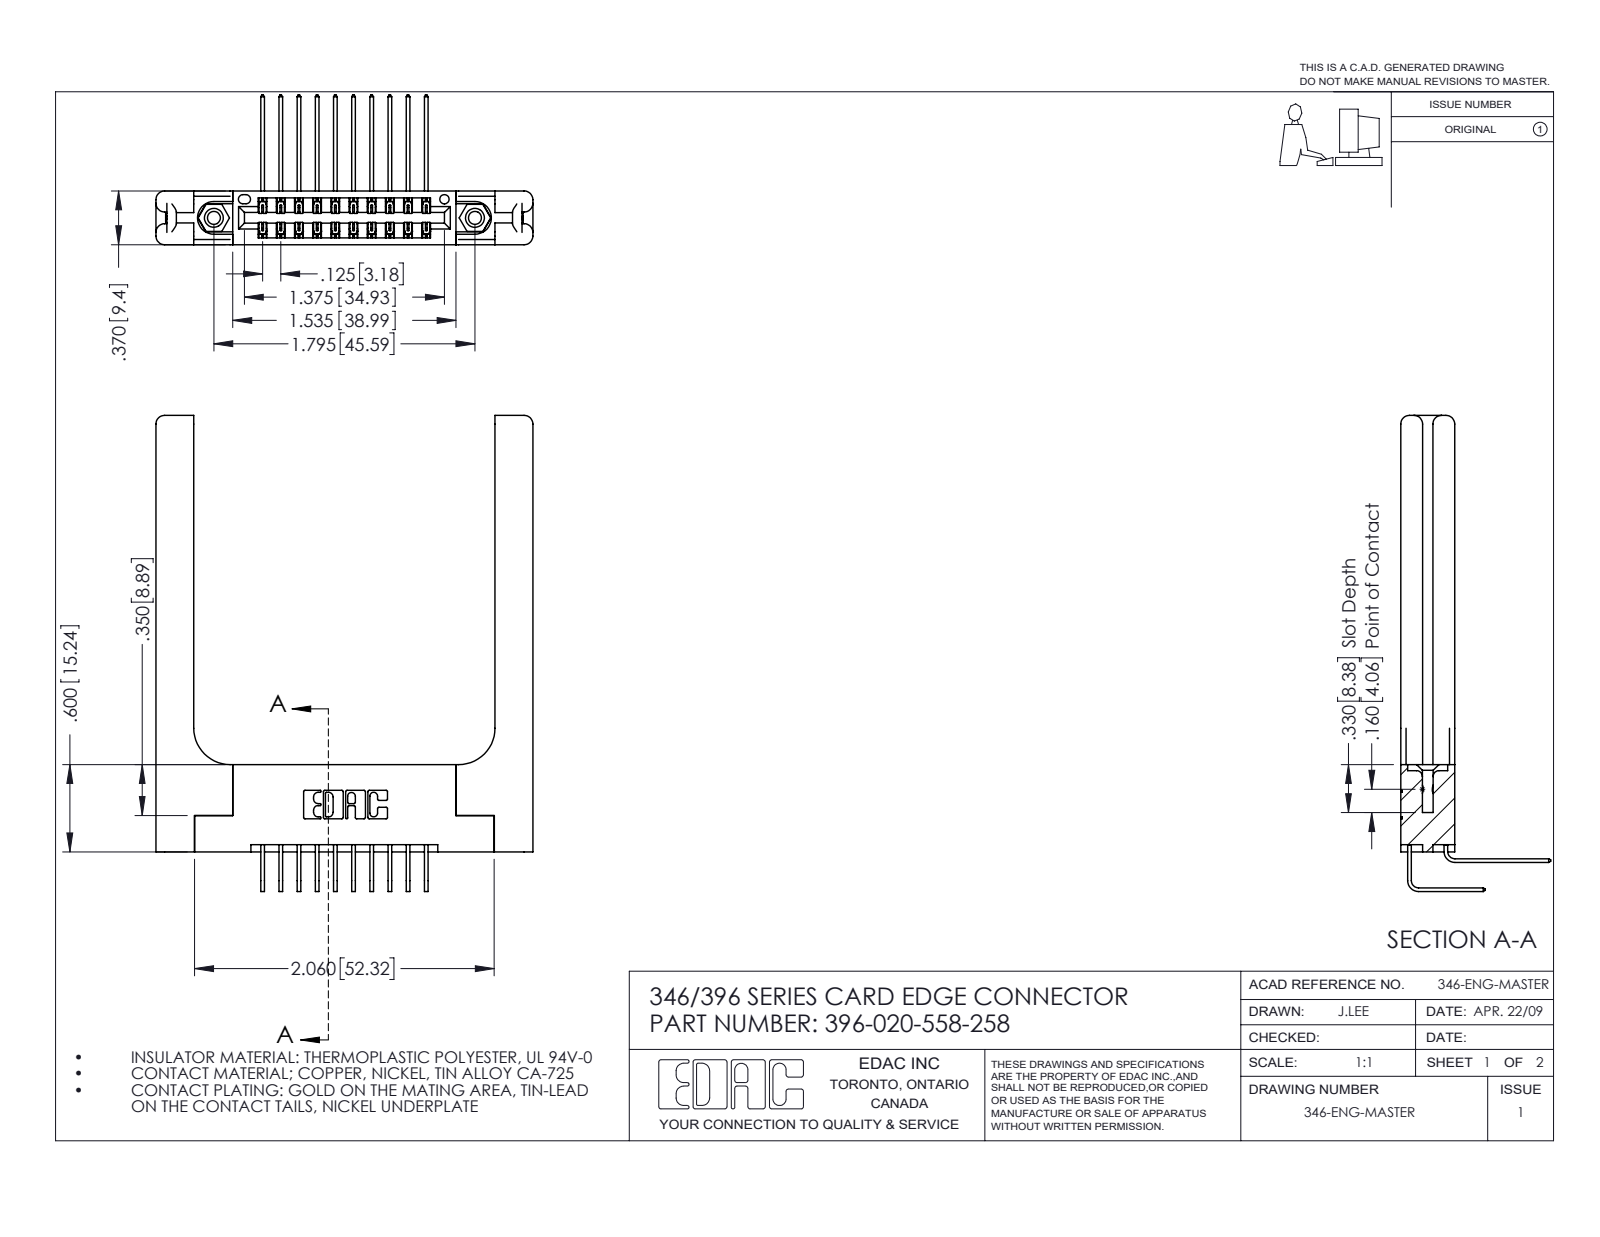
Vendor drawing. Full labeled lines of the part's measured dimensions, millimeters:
Part name (STEP PRODUCT): 345-250-001_345-250-001-102; 396-020-558-258; 346-220-058_345-220-058; 345-292-001_558 Tail - 2 (+2 more)
STEP written by: SolidWorks 2016 (CONFIG_CONTROL_DESIGN)
Units: millimetres
Bodies: 25 solids, 1458 faces (964 planar, 434 cylindrical, 60 other)
Overall size (bounding box): 83.1 × 65.8 × 26.2
Volume: 13 800 mm³ · Surface area: 13 660 mm²
Round holes (diameter × count): ⌀2.3 ×2, ⌀3.2 ×2, ⌀4 ×2, ⌀1.6 ×1
Round bosses / shafts (diameter × count): ⌀3.9 ×2
Partial cylindrical surfaces — rounded edges, fillets, slot ends (radius × count): R0.2 ×30, R0.3 ×22, R1.5 ×16, R0.2 ×6, R0.8 ×6, R0.7 ×3, R0.4 ×2, R0.6 ×2
Main face-to-face distances: 9.4, 3.8, 1.8, 8.2, 1.2, 3.8, 5.6, 6.4, 2.6, 4.4
Hole centre spacings: 6.2, 40.4, 45.6
